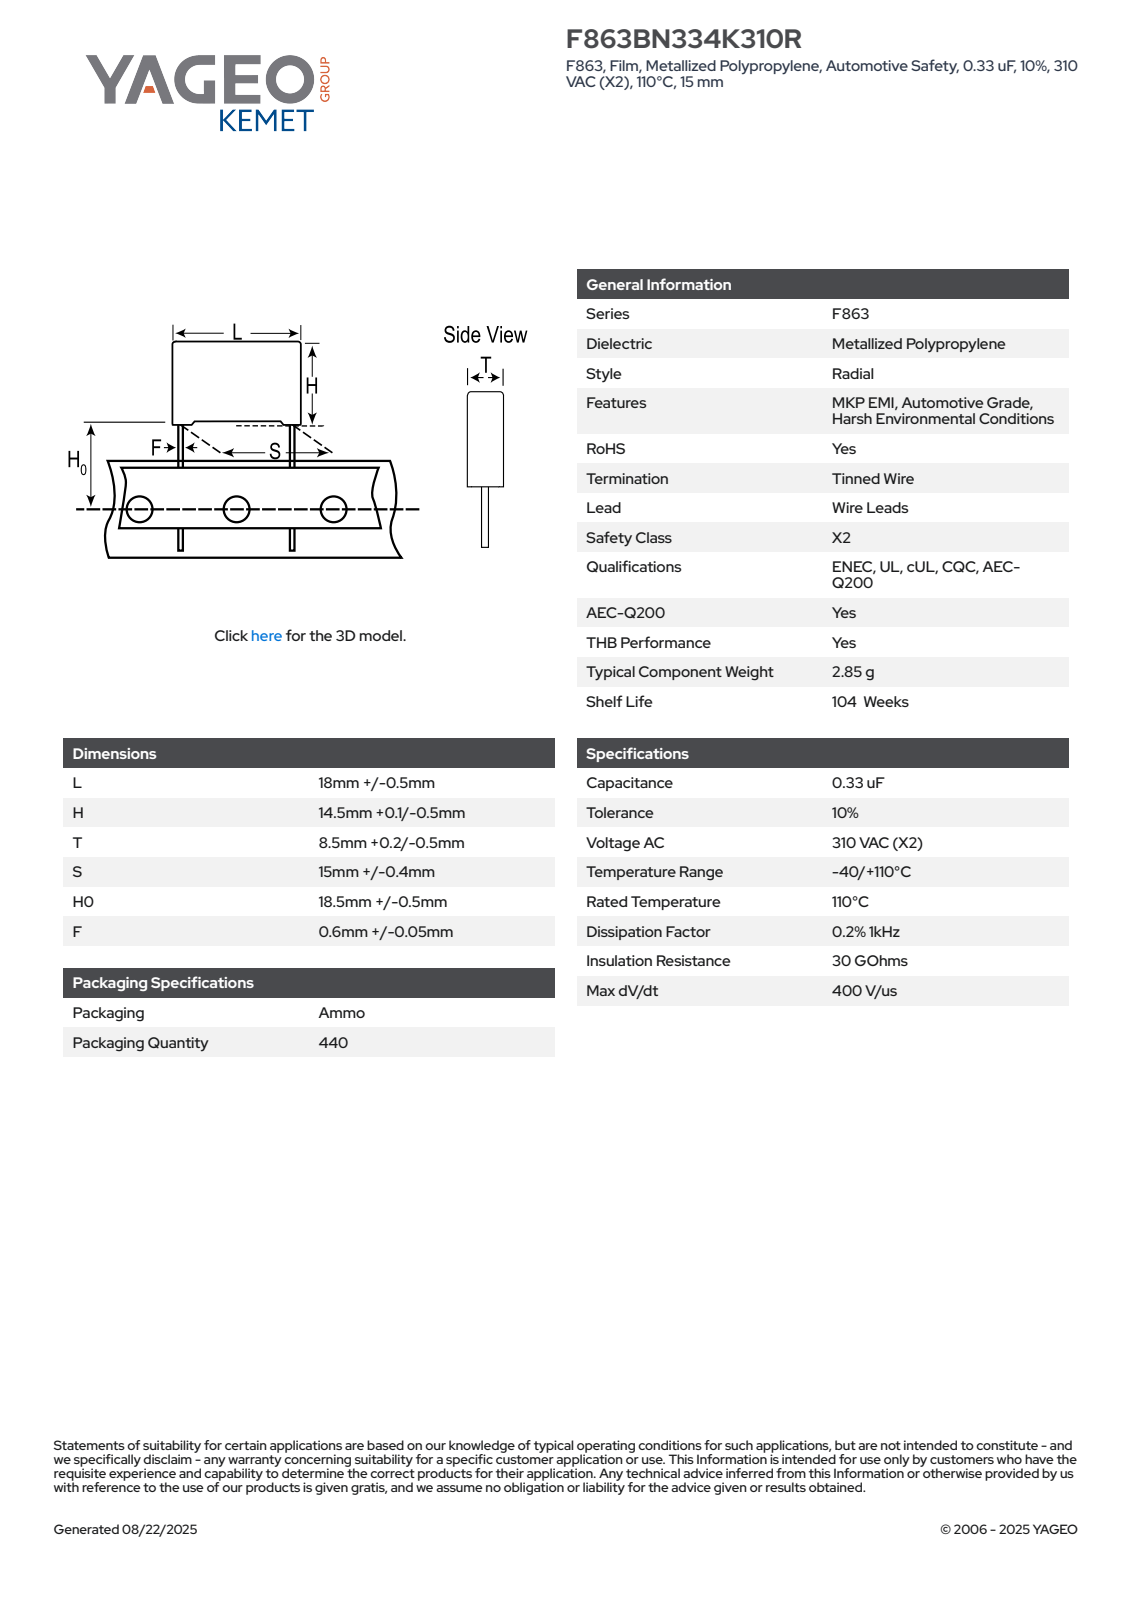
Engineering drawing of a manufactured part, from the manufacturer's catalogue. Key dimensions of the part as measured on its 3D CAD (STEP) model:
Part name (STEP PRODUCT): CFR_RB2_18X14.5X8.5_L18.5H14.6T8.7S15H019F0.65
STEP written by: SolidWorks 2020 (AUTOMOTIVE_DESIGN)
Units: millimetres
Bodies: 4 solids, 85 faces (77 planar, 8 cylindrical, 0 other)
Overall size (bounding box): 33.6 × 18.5 × 8.71
Volume: 2 256 mm³ · Surface area: 1 225 mm²
Round bosses / shafts (diameter × count): ⌀0.65 ×2
Partial cylindrical surfaces — rounded edges, fillets, slot ends (radius × count): R0.5 ×4
Main face-to-face distances: 8.7, 13.85, 18.5, 0.62, 0.75, 14.6, 8.08, 0.5, 14.1, 17.88
